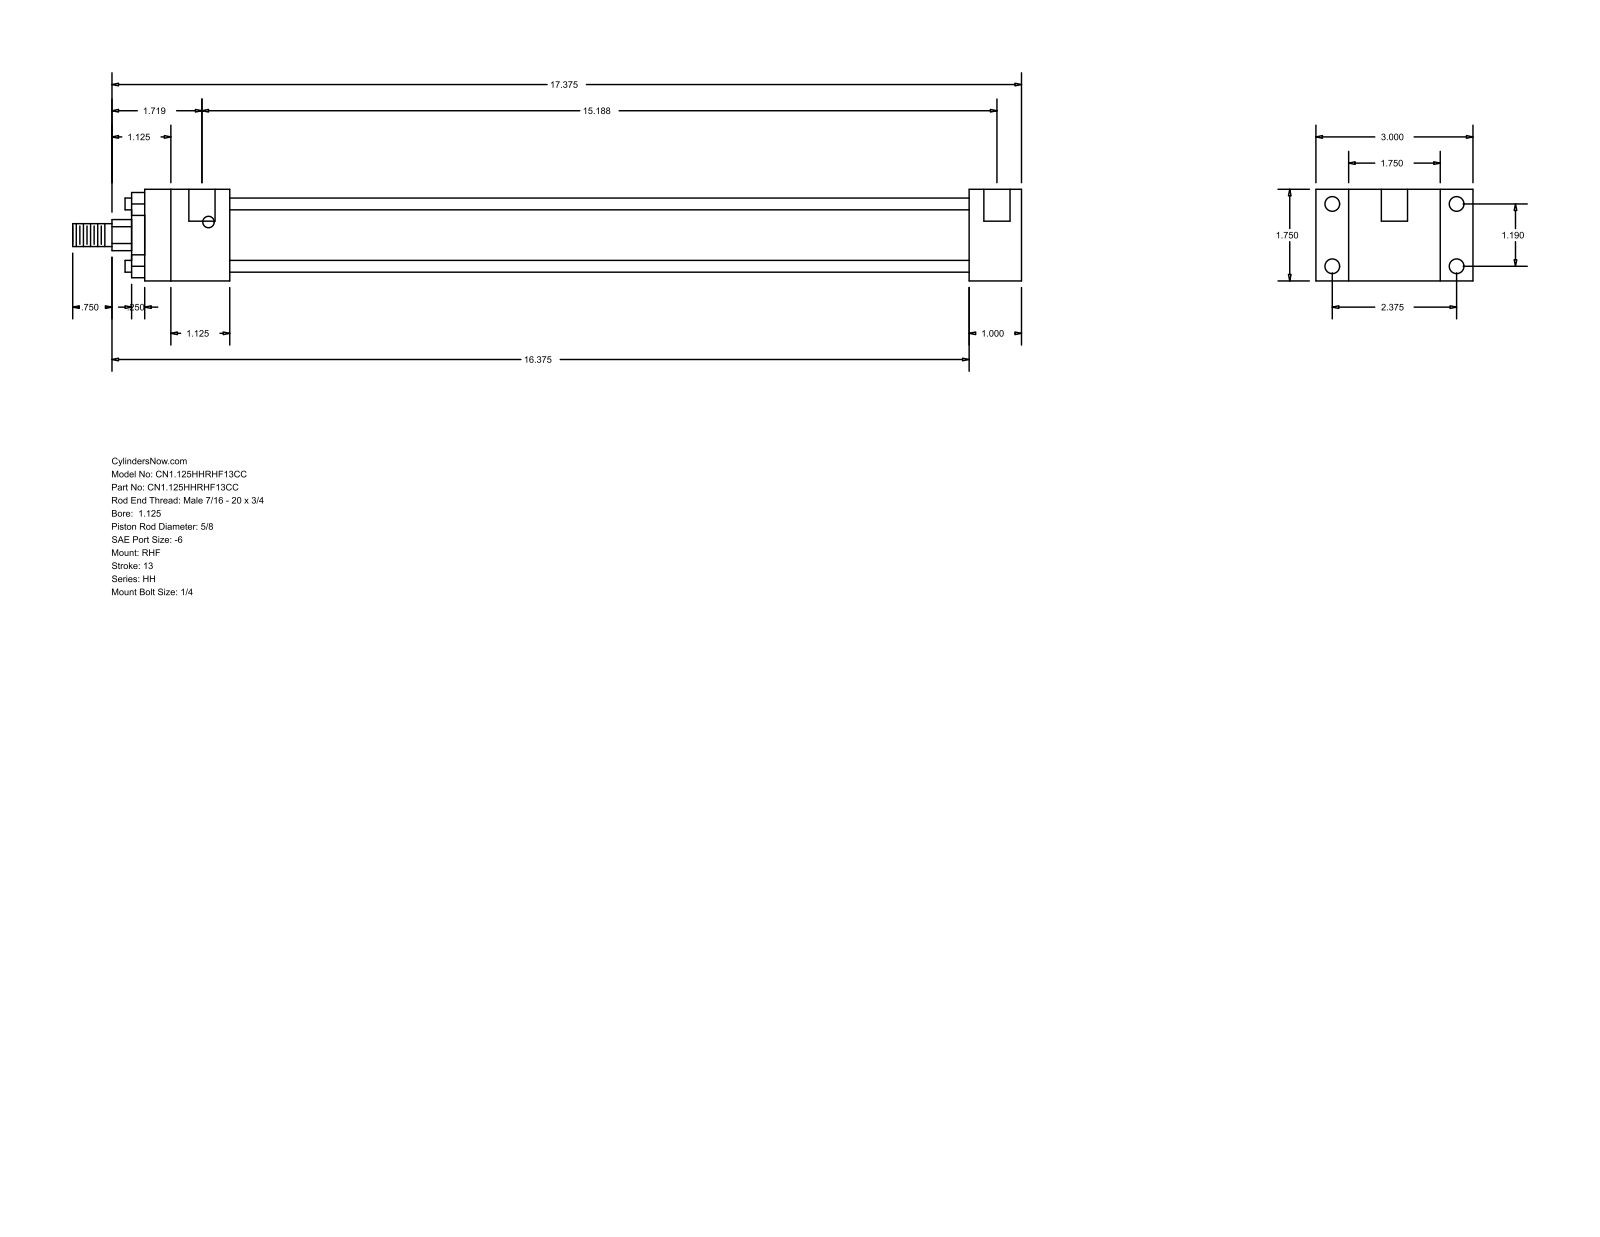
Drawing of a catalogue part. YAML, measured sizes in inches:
part_name: "HH_RHF__0112_0.625"
step_written_by: "GSSL Pune (CONFIG_CONTROL_DESIGN)"
units: inches
bodies: {solids: 0, faces: 88, planar: 60, cylindrical: 28, other: 0}
overall_size: [18.125, 3, 1.75]
round_holes:
  - {diameter: 0.219, count: 4}
  - {diameter: 0.281, count: 4}
  - {diameter: 0.5, count: 2}
round_bosses_or_shafts:
  - {diameter: 0.225, count: 4}
  - {diameter: 1.375, count: 1}
  - {diameter: 1.125, count: 1}
  - {diameter: 0.625, count: 1}
  - {diameter: 0.437, count: 1}
partial_cylinders:
  - {radius: 0.297, count: 1}
face_to_face_distances: [1.75, 0.625, 2.375, 1, 3, 14.125, 15.125, 1.625, 15.75, 16.75]
hole_center_spacings: [1.19, 2.375, 2.656, 15.063, 0.125, 15.187]
